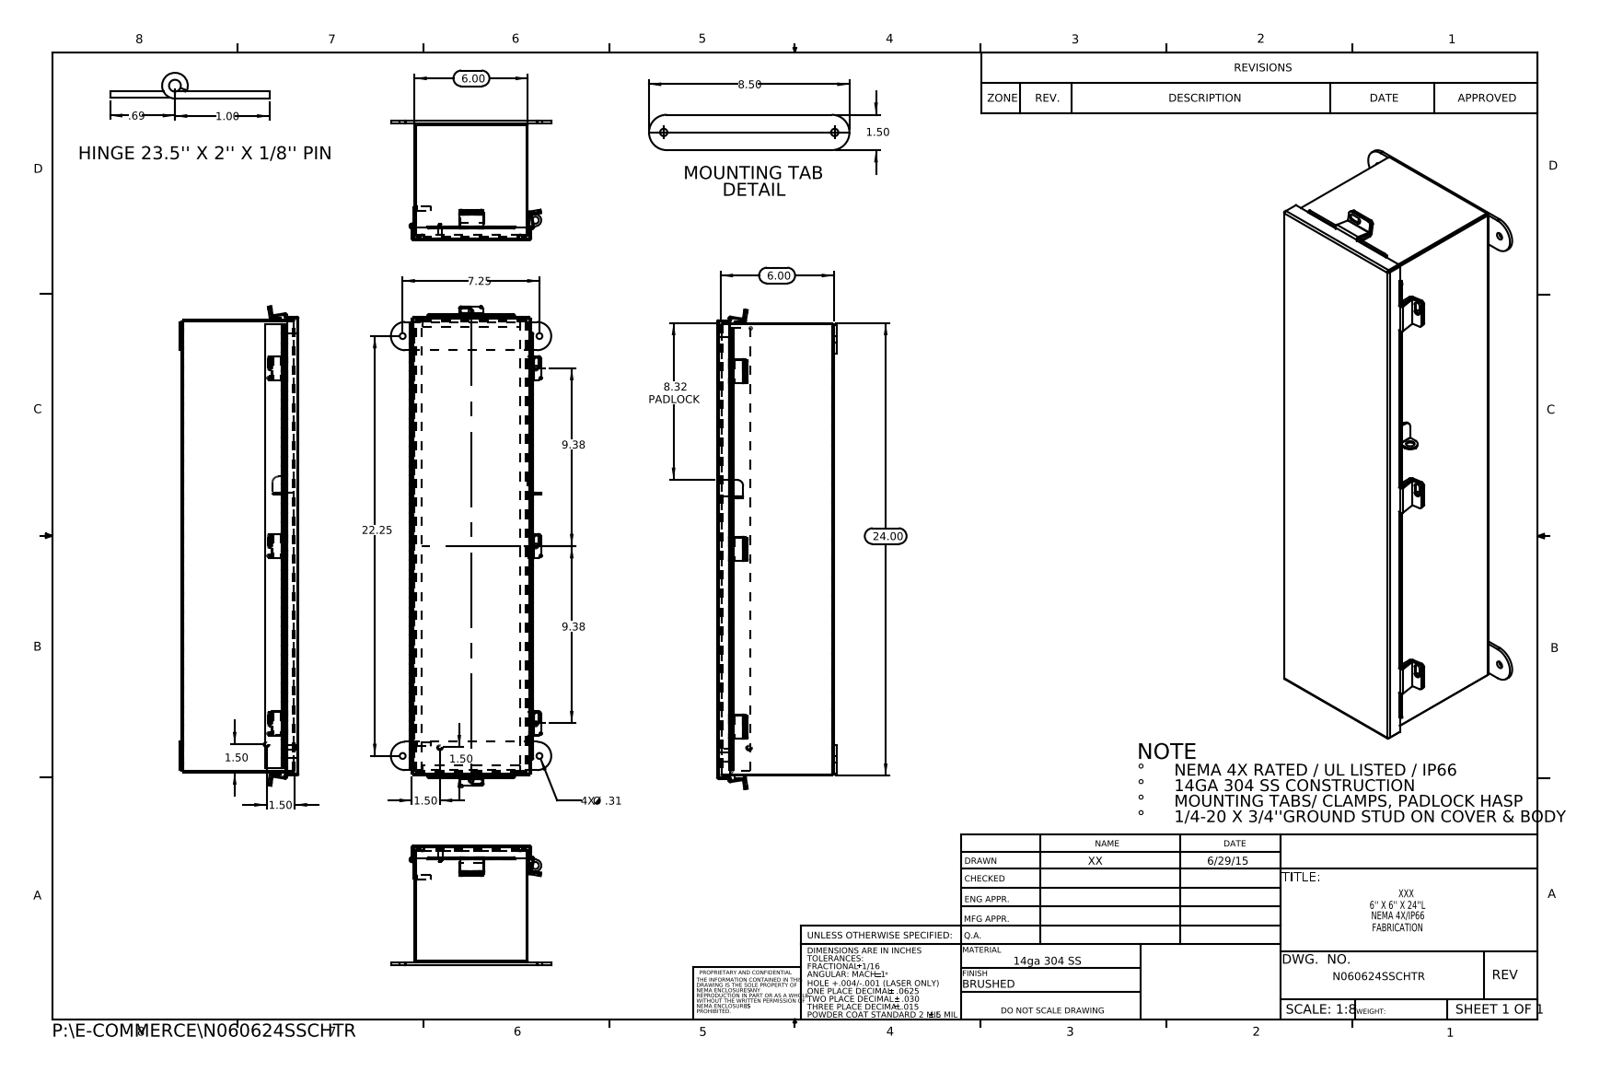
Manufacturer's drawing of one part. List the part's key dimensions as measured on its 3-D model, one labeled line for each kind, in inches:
Part name (STEP PRODUCT): HW-CLH-JH-20154; N060624SSCHTR HW-CD-S-25020-034; N060624SSCHTR JIC Bottom; N060624SSCHTR JIC Top (+8 more)
STEP written by: SolidWorks 2015 (CONFIG_CONTROL_DESIGN)
Units: inches
Bodies: 21 solids, 886 faces (545 planar, 321 cylindrical, 20 other)
Overall size (bounding box): 25.407 × 8.5 × 6.337
Volume: 60.64 in³ · Surface area: 1 623 in²
Round holes (diameter × count): ⌀0.25 ×5, ⌀0.313 ×4, ⌀0.125 ×1, ⌀0.375 ×1
Round bosses / shafts (diameter × count): ⌀0.315 ×2, ⌀0.236 ×2, ⌀0.273 ×1, ⌀0.25 ×1
Partial cylindrical surfaces — rounded edges, fillets, slot ends (radius × count): R0.125 ×17, R0.009 ×12, R0.013 ×11, R0.088 ×11, R0.133 ×10, R0.083 ×6, R0.1 ×6, R0.75 ×4
Main face-to-face distances: 0.075, 5.925, 6.128, 6, 5.85, 6.203, 6.053, 23.925, 0.149, 6.074
Hole centre spacings: 7.25, 9.425, 22.25, 23.402, 6.543, 18.85
